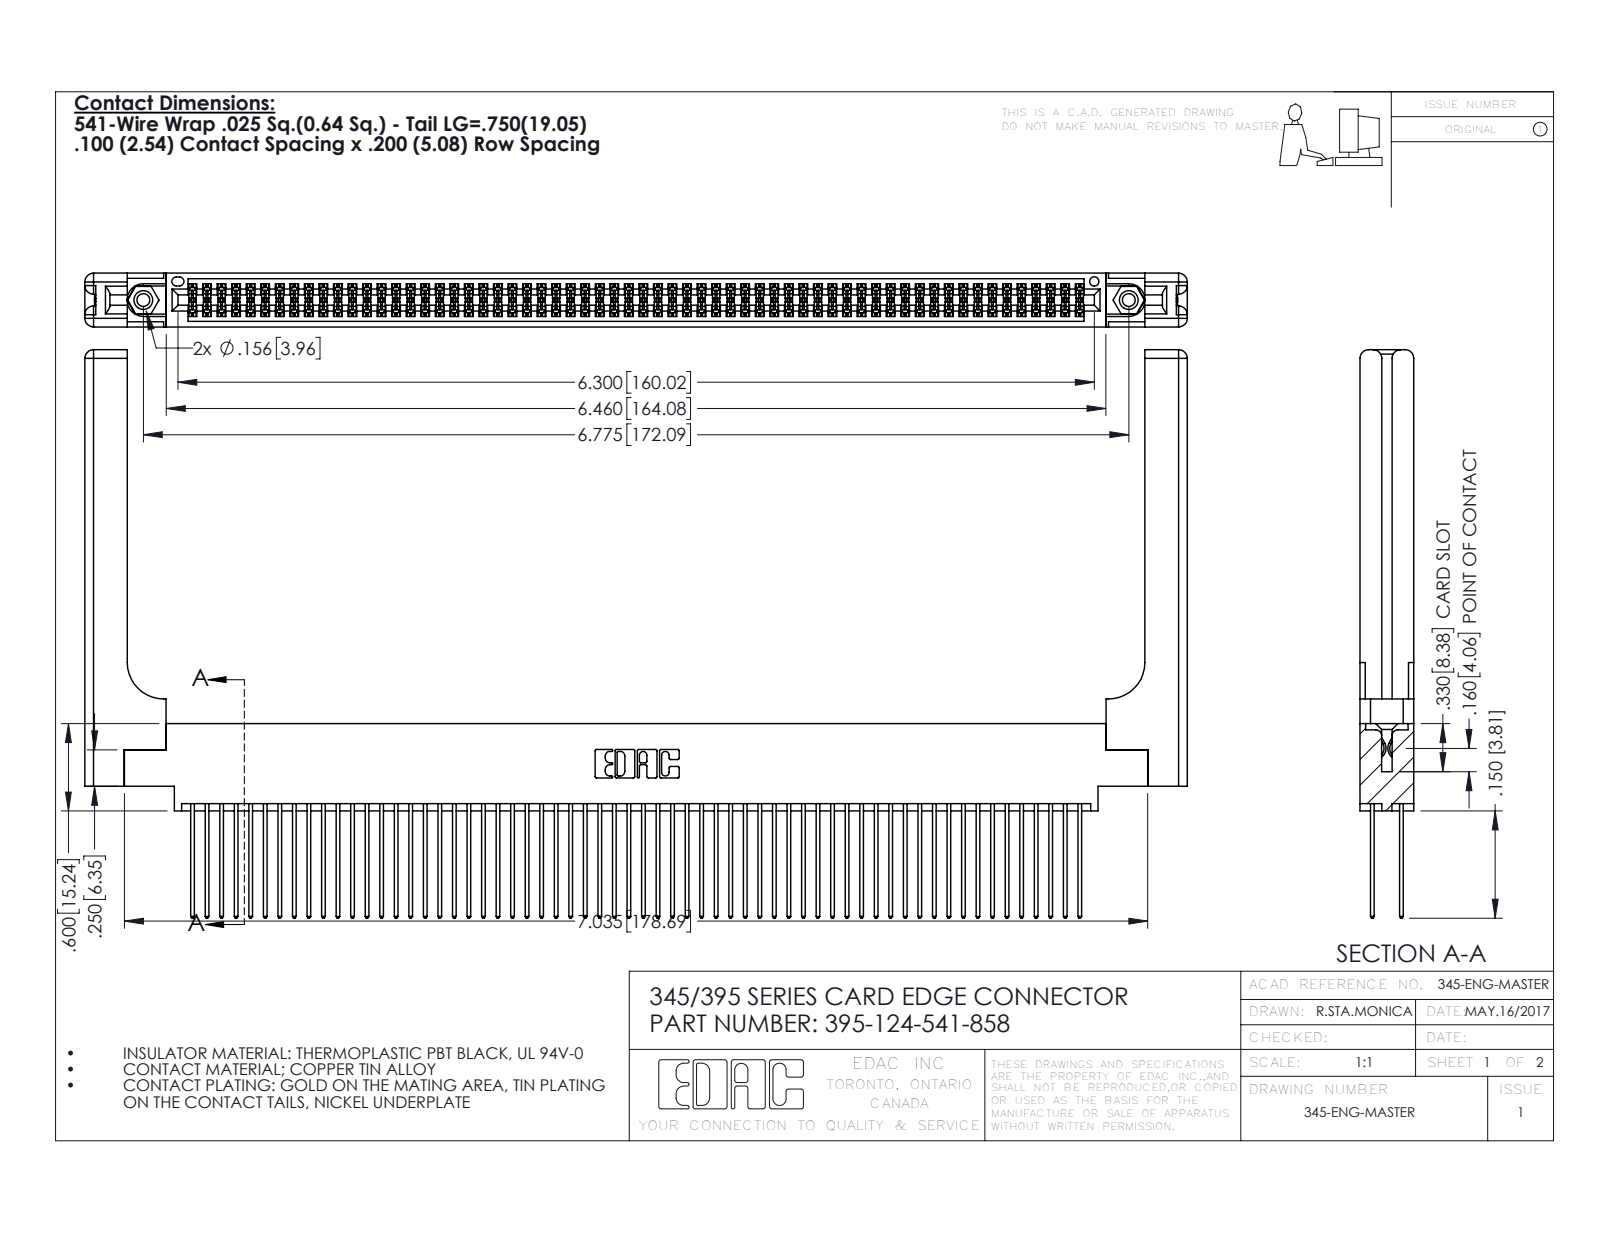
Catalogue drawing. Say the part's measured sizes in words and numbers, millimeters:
The part is named "345-220-058_345-220-058; 345 Part_0.170 Offset - 0.156 Dia-TH; 345-292-001_345-293-141; 345-250-001_345-250-001-102 (+1 more)". Its 3-D file was written by "SolidWorks 2016 (CONFIG_CONTROL_DESIGN)". It is 129 solids with 6586 faces: 4324 planar, 2202 cylindrical and 60 other. Overall it measures 192.5 by 99.2 by 9.4 millimeters. Its volume is 27 960 cubic millimeters and its surface area 37 740 square millimeters. Round holes: 2 of diameter 2.3, 2 of diameter 3.2, 2 of diameter 4, 1 of diameter 1.6. Round bosses or shafts: 2 of diameter 3.9. Partial cylindrical surfaces (rounded edges, fillets, slot ends): 186 of radius 0.2, 124 of radius 0.3, 22 of radius 0.3, 16 of radius 1.5, 6 of radius 0.2, 6 of radius 0.8, 3 of radius 0.7, 2 of radius 0.4. The main face-to-face distances are 1.8, 7.6, 9.4, 2.5, 6.9, 0.6, 5.1, 5.7, 4.4, 3.8. The hole center spacings are 6.9, 166.1, 172.1.
